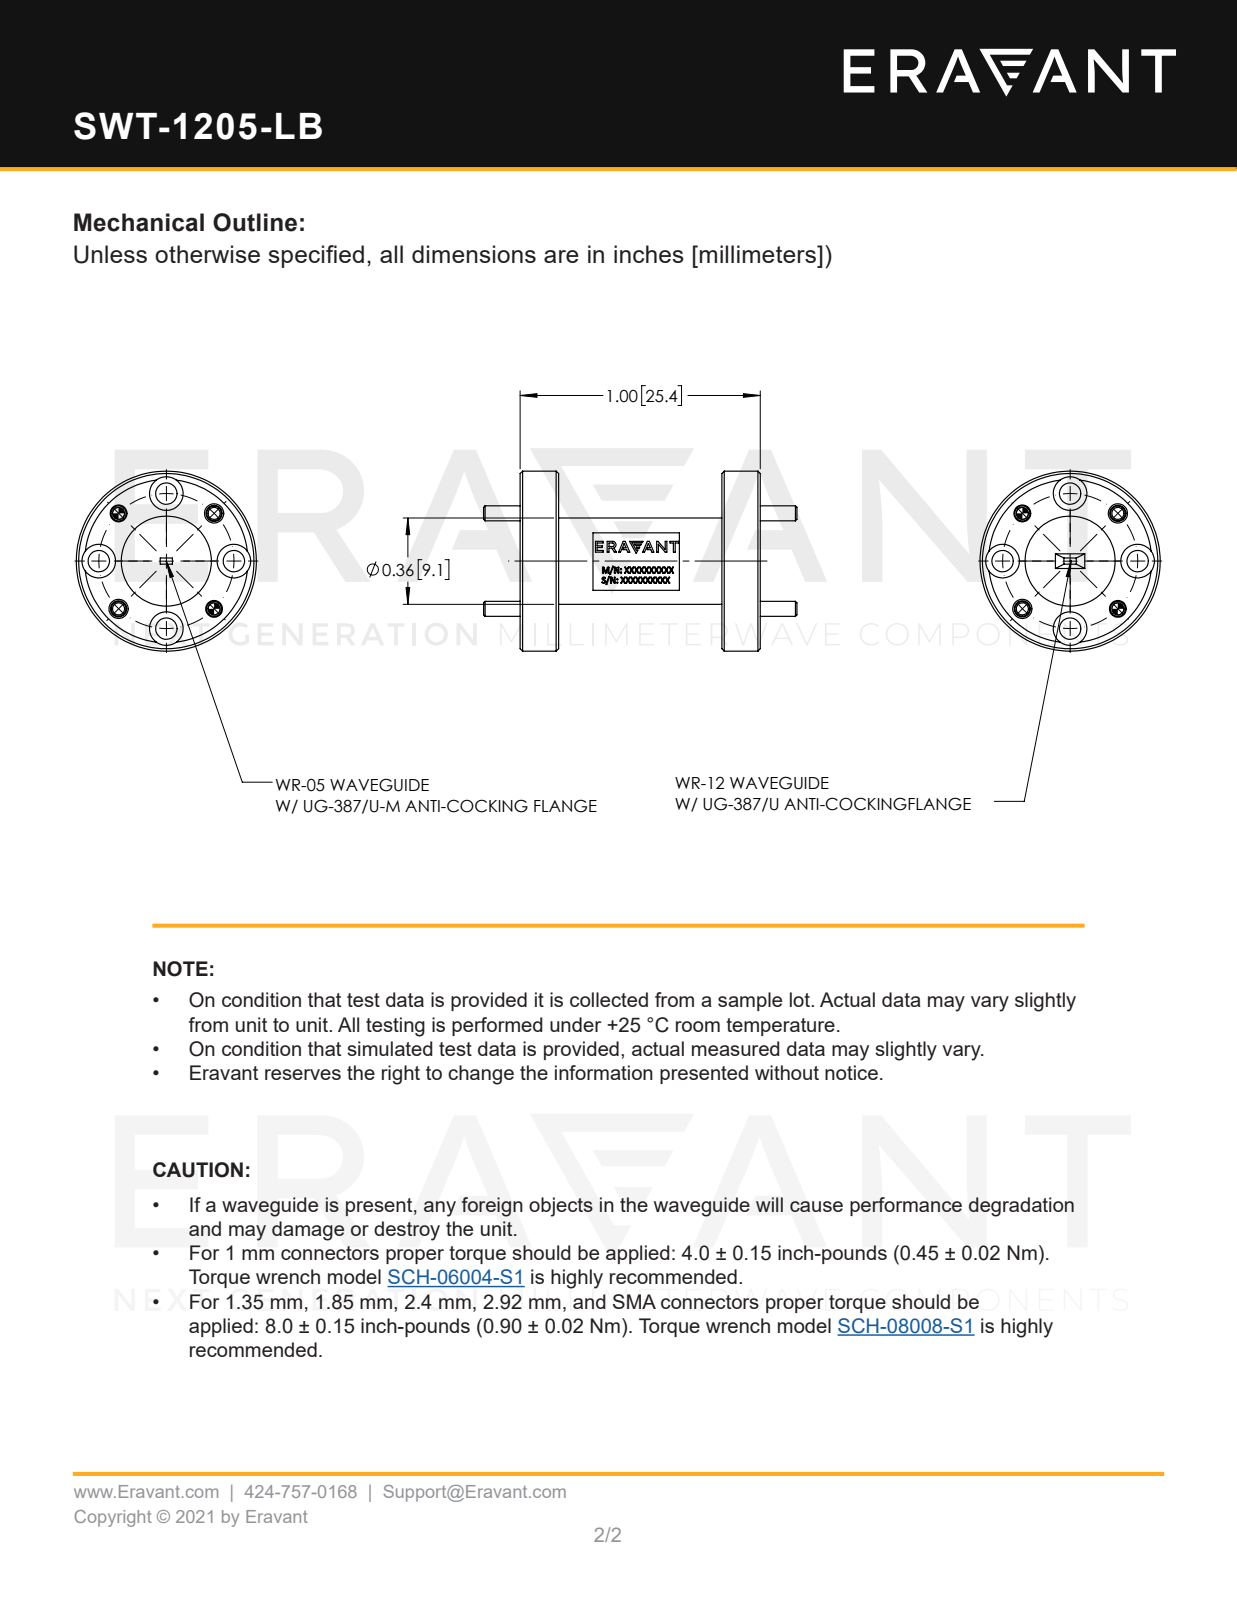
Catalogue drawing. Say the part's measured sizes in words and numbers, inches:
The part is named "SWT-1205-LB". Its 3-D file was written by "SolidWorks 2021 (CONFIG_CONTROL_DESIGN)". It is 5 solids with 148 faces: 34 planar, 74 cylindrical and 40 other. Overall it measures 1.305 by 0.75 by 0.75 inches. Its volume is 0.19 cubic inches and its surface area 3.868 square inches. Round holes: 4 of diameter 0.061, 4 of diameter 0.067, 4 of diameter 0.089, 4 of diameter 0.14, 1 of diameter 0.68. Round bosses or shafts: 4 of diameter 0.063, 1 of diameter 0.75, 1 of diameter 0.375, 1 of diameter 0.36. The main face-to-face distances are 0.14, 0.82, 0.02, 0.16, 0.84, 0.98, 0.68, 0.96, 1, 0.06. The hole center spacings are 0.215, 0.281, 0.398, 0.519, 0.562.
